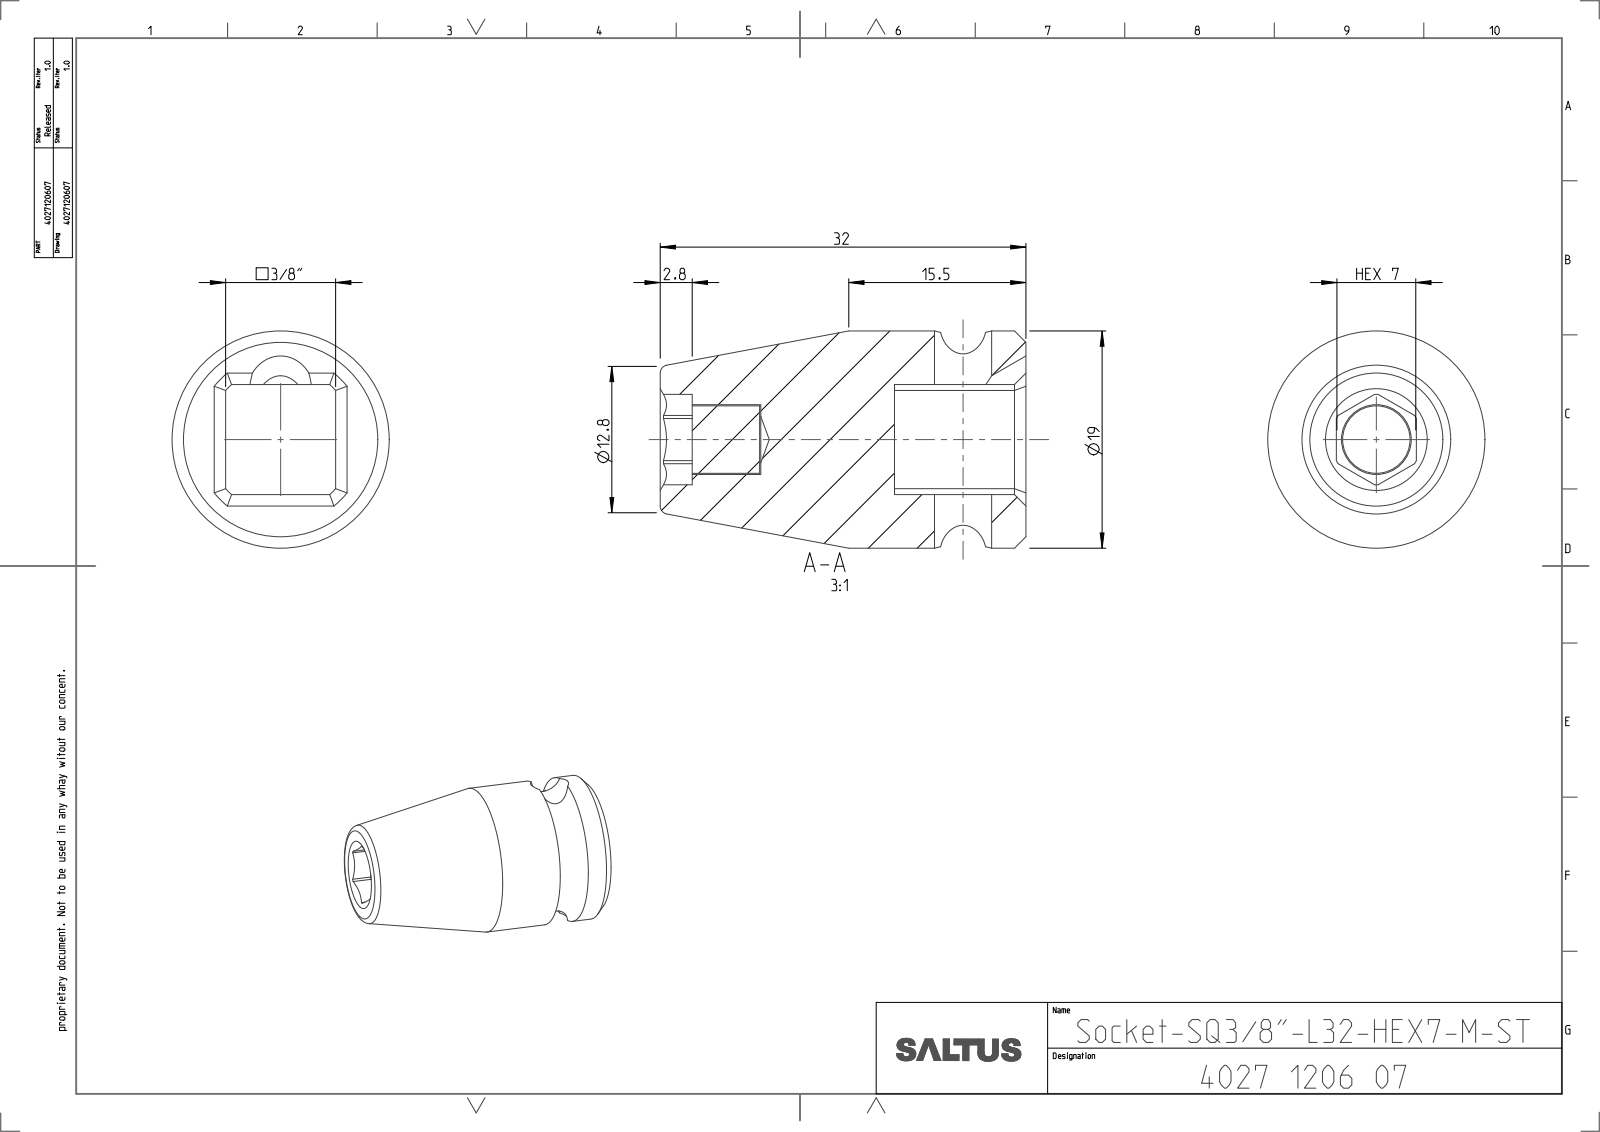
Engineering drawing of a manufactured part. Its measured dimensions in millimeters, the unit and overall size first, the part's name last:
Units: millimetres
Overall size (bounding box): 32 × 19 × 19
Round holes (diameter × count): ⌀5 ×1, ⌀6.1 ×1
Round bosses / shafts (diameter × count): ⌀19 ×1, ⌀5.9 ×1
Partial cylindrical surfaces — rounded edges, fillets, slot ends (radius × count): R3 ×1, R3.96 ×1, R6.45 ×1
Main face-to-face distances: 9.62, 11.5, 32, 20.5, 29.2, 17.7, 2.8, 23.3, 11.8, 5.9
Volume: 6 048 mm³ · Surface area: 2 964 mm²
Bodies: 2 solids, 61 faces (22 planar, 23 cylindrical, 16 other)
Part name (STEP PRODUCT): 4027120607
STEP written by: CREO PARAMETRIC BY PTC INC, 2022414 (CONFIG_CONTROL_DESIGN)
